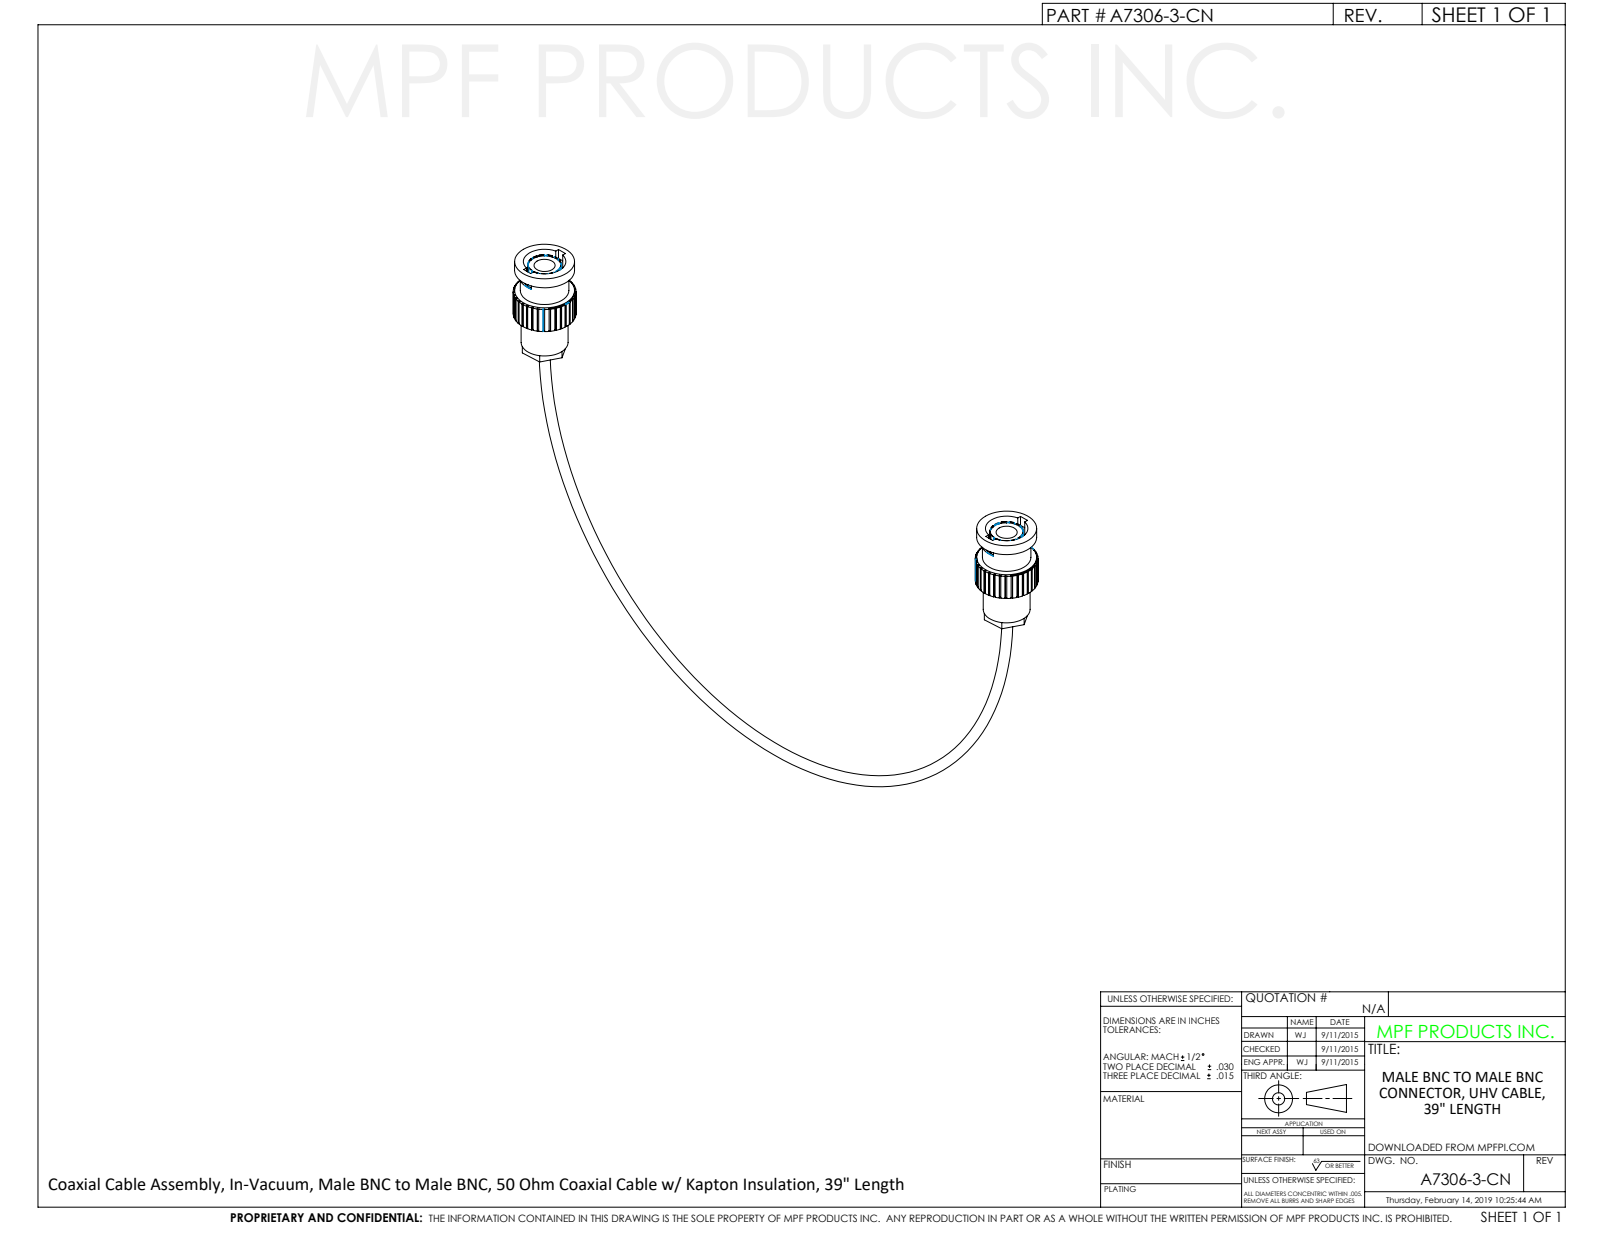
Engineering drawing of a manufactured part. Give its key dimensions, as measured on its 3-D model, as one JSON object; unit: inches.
{"part_name": "A7306-3-CN", "step_written_by": "SolidWorks 2012 (CONFIG_CONTROL_DESIGN)", "units": "inches", "bodies": {"solids": 0, "faces": 519, "planar": 360, "cylindrical": 157, "other": 2}, "overall_size": [6.565, 4.028, 0.575], "round_holes": [[0.158, 2], [0.194, 2], [0.39, 2]], "round_bosses_or_shafts": [[0.55, 2], [0.525, 2], [0.43, 2], [0.308, 2], [0.445, 1], [0.445, 1], [0.101, 1]], "partial_cylinders_radius": [[0.15, 2], [0.151, 2], [0.287, 2], [0.068, 1]], "face_to_face_distances": [0.978, 0.014, 0.653, 0.325, 0.878, 0.225, 0.1, 0.385, 0.268, 0.493], "hole_center_spacings": [5.99]}
